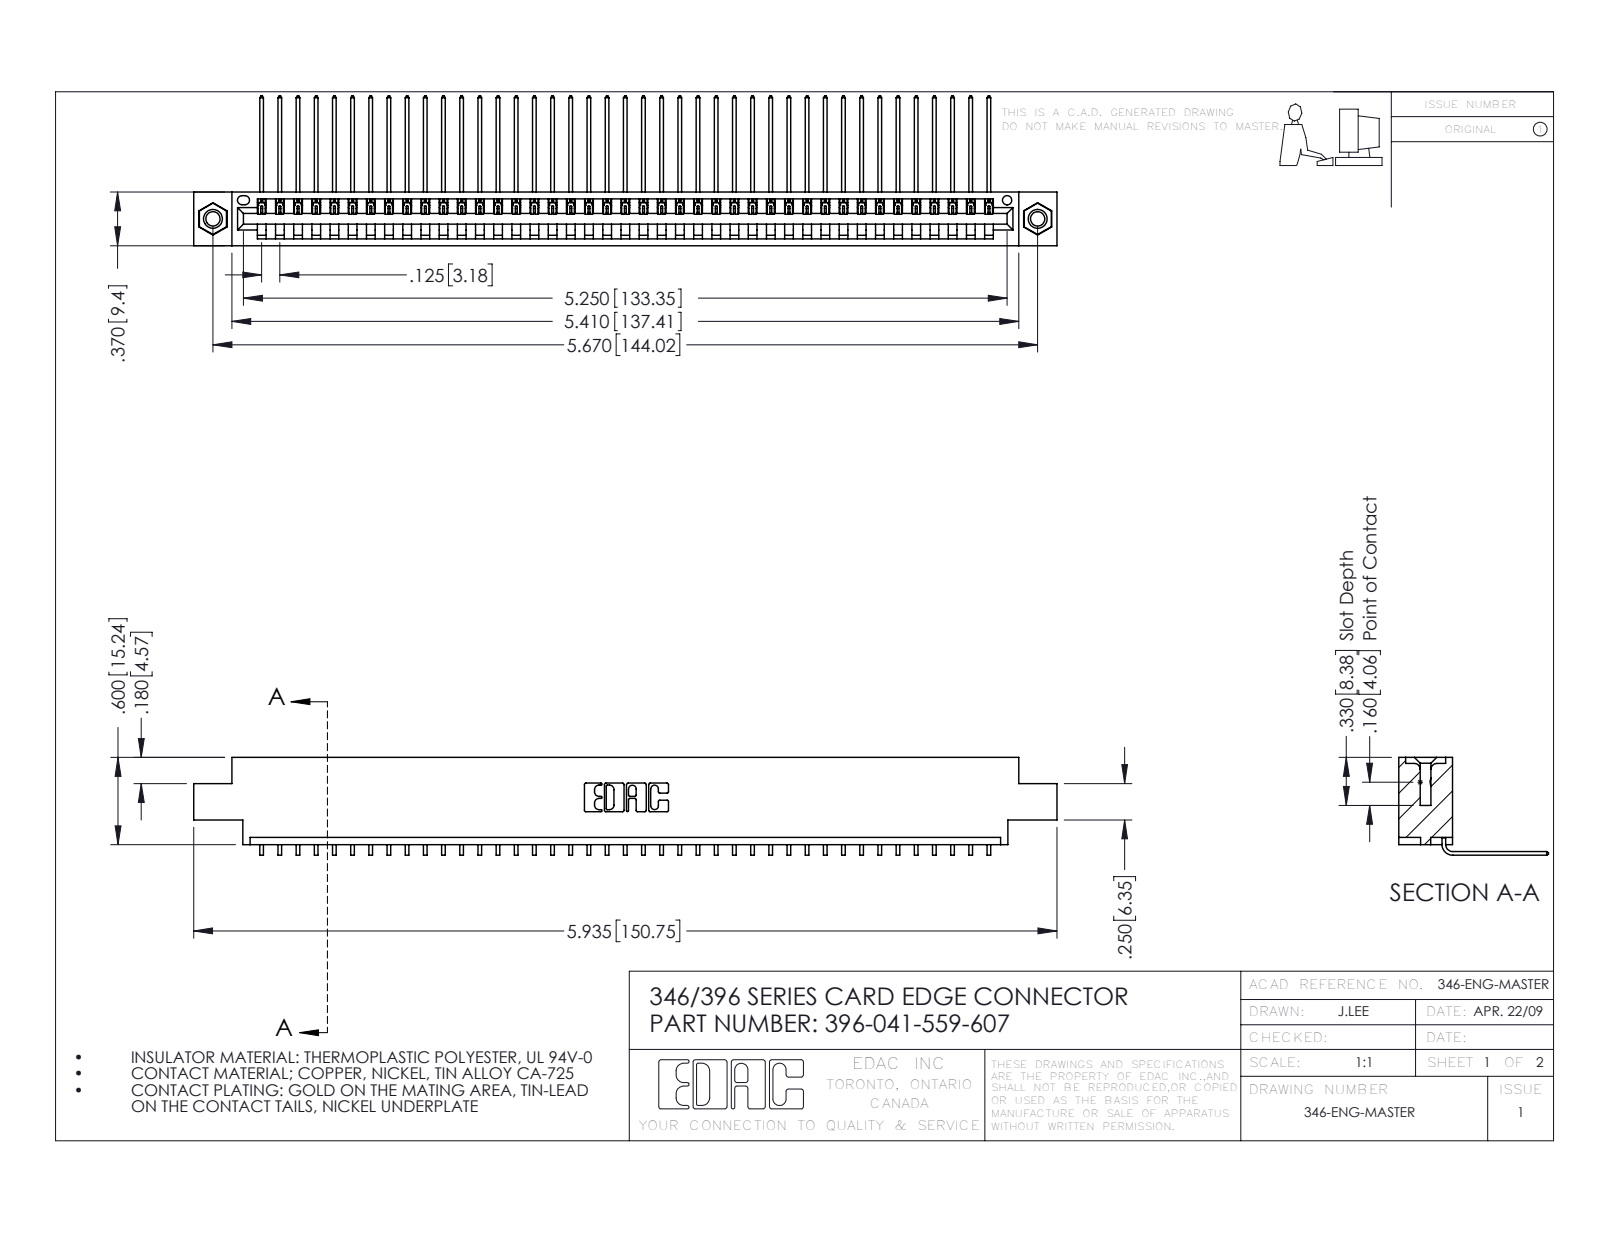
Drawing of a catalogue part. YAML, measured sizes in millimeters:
part_name: "345-292-001_558 559 Tail - 1; 396-041-559-607; 346 Part_0.170 Offset - 0.156 Dia-TI; 345-250-001_345-250-005-103"
step_written_by: "SolidWorks 2016 (CONFIG_CONTROL_DESIGN)"
units: millimeters
bodies: {solids: 44, faces: 2646, planar: 1834, cylindrical: 796, other: 16}
overall_size: [150.7, 26.2, 17.1]
volume: 14400
surface_area: 18990
round_holes:
  - {diameter: 2.5, count: 2}
  - {diameter: 3.2, count: 2}
  - {diameter: 4, count: 2}
  - {diameter: 1.6, count: 1}
round_bosses_or_shafts:
  - {diameter: 3.9, count: 2}
partial_cylinders:
  - {radius: 0.2, count: 82}
  - {radius: 0.3, count: 22}
  - {radius: 0.2, count: 6}
  - {radius: 0.8, count: 6}
  - {radius: 0.7, count: 3}
  - {radius: 0.8, count: 2}
  - {radius: 1, count: 2}
  - {radius: 0.4, count: 1}
face_to_face_distances: [1.2, 8.2, 9.4, 0.6, 6.4, 1.8, 5.6, 3.8, 7.6, 2.5]
hole_center_spacings: [6.2, 138.7, 144]
